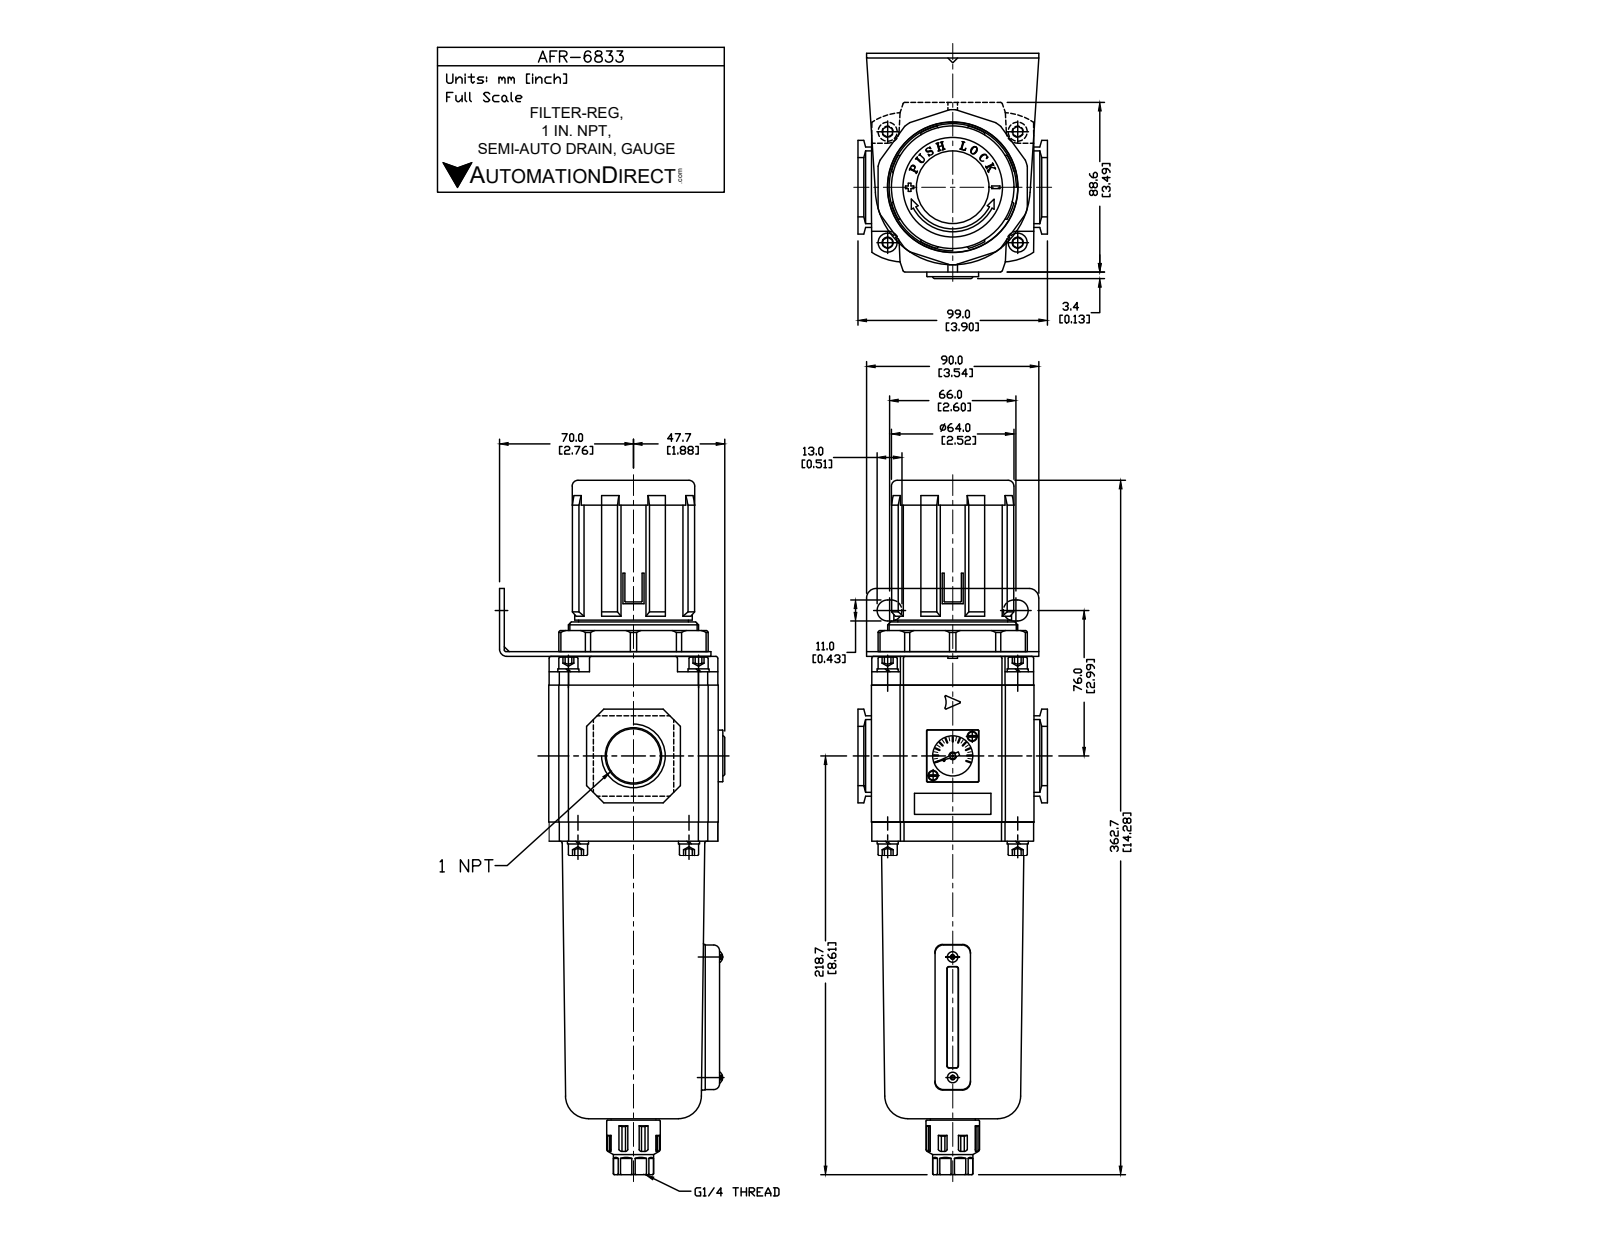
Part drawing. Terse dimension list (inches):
name: AFR-6833
written by: SolidWorks 2015 (CONFIG_CONTROL_DESIGN)
unit: in
bodies: 16 solids, 703 faces (439 planar, 175 cylindrical, 89 other)
size: 14.28 × 4.606 × 3.898
volume: 101.5 in³; area: 289.1 in²
holes: 6× ⌀0.118, 1× ⌀0.079, 1× ⌀0.472, 1× ⌀1.141, 1× ⌀1.181, 1× ⌀1.496
bosses: 8× ⌀0.394, 2× ⌀0.217, 2× ⌀0.106, 1× ⌀2.677, 1× ⌀2.52, 1× ⌀2.441, 1× ⌀2.117, 1× ⌀1.102
rounds: 12× R0.039, 10× R0.047, 8× R0.051, 8× R0.098, 8× R0.374, 8× R0.783, 6× R0.02, 4× R0.012
face distances: 0.098, 3.591, 3.492, 3.449, 0.039, 3.488, 3.346, 3.622, 0.394, 0.138
hole spacings: 1.628, 1.365, 2.093, 2.494, 3.256, 2.73
